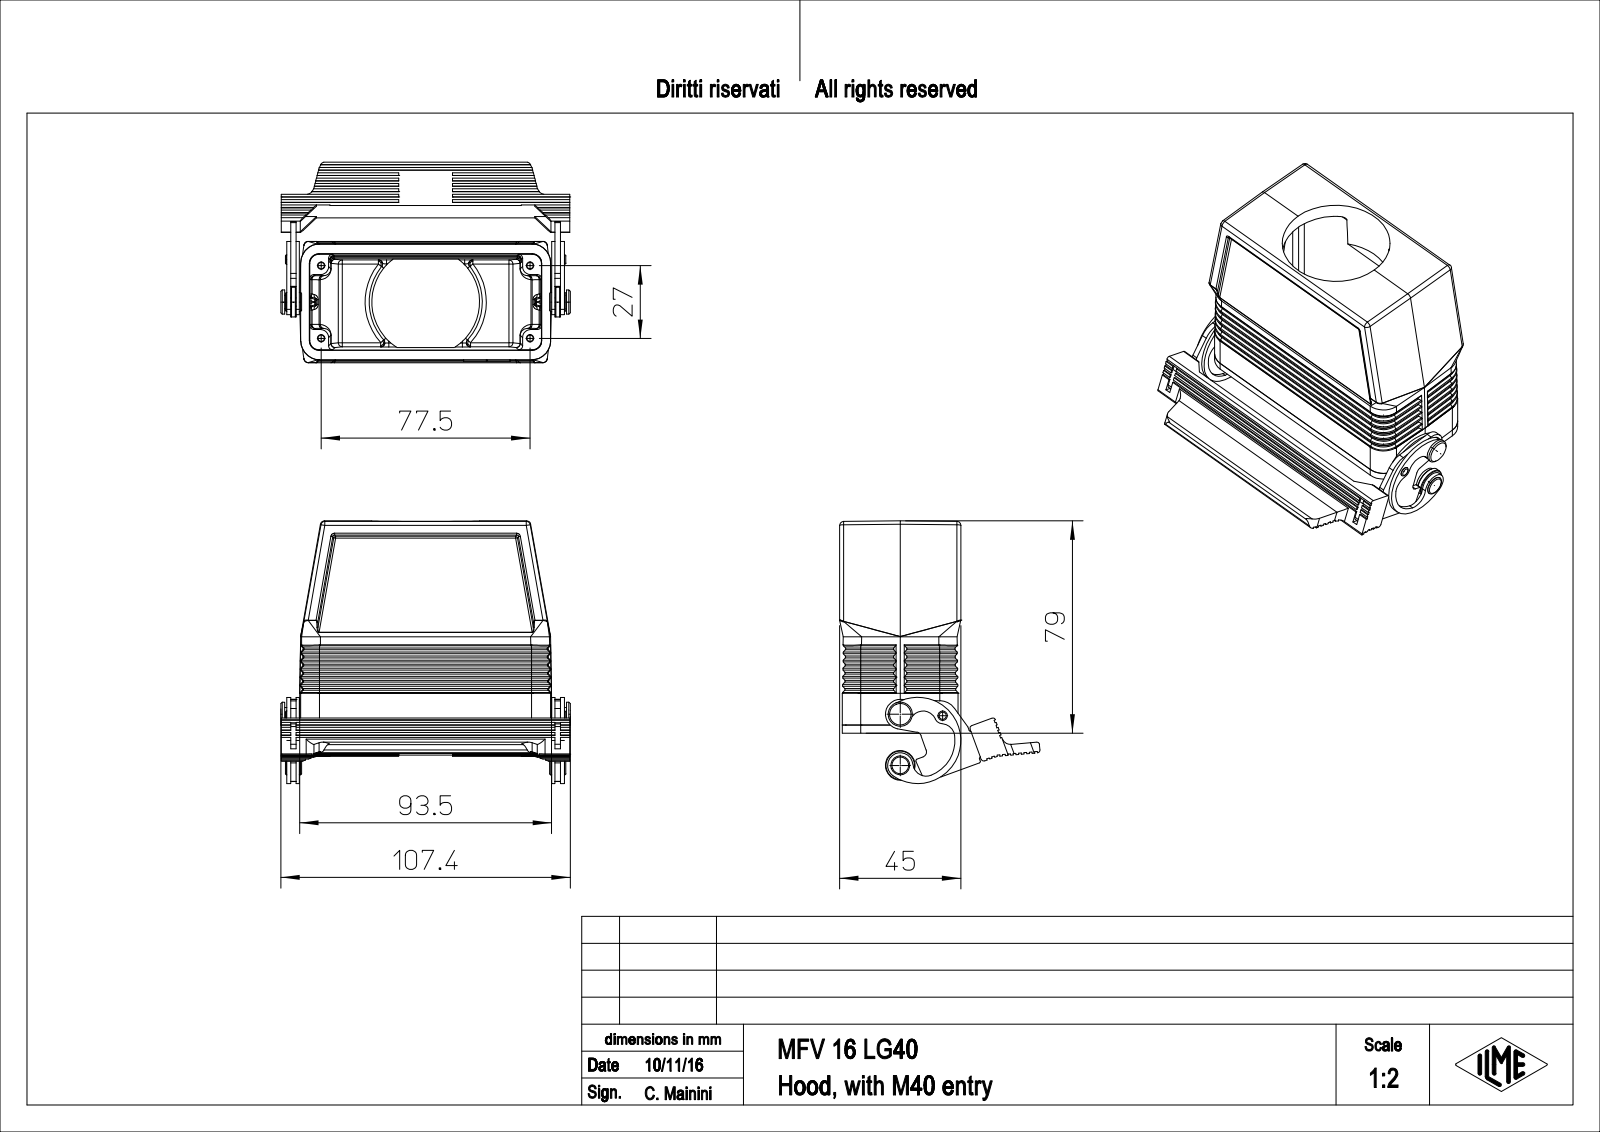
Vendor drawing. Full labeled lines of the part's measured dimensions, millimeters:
Part name (STEP PRODUCT): MFV_16_LG40
STEP written by: PTC Creo Elements/Direct Modeling 19.0E 27-Jun-2016 (C) Parametric Technology GmbH (AUTOMOTIVE_DESIGN)
Units: millimetres
Bodies: 1 solid, 854 faces (440 planar, 262 cylindrical, 152 other)
Overall size (bounding box): 107.4 × 97.5 × 74.37
Volume: 110 898 mm³ · Surface area: 58 024 mm²
Round holes (diameter × count): ⌀2.75 ×4, ⌀3.1 ×1, ⌀4 ×1, ⌀5 ×1, ⌀40 ×1
Round bosses / shafts (diameter × count): ⌀11 ×1, ⌀9 ×1, ⌀7 ×1, ⌀5 ×1, ⌀3.5 ×1, ⌀3 ×1
Partial cylindrical surfaces — rounded edges, fillets, slot ends (radius × count): R0.5 ×82, R1.5 ×13, R7 ×9, R3 ×8, R1 ×5, R3.5 ×4, R3.5 ×4, R4.2 ×4
Main face-to-face distances: 1, 2, 43, 4, 3.5, 98.1, 7, 6, 3, 0.5
Hole centre spacings: 27, 41.02, 41.03, 77.49, 82.06, 19.11, 24.25, 34.06
